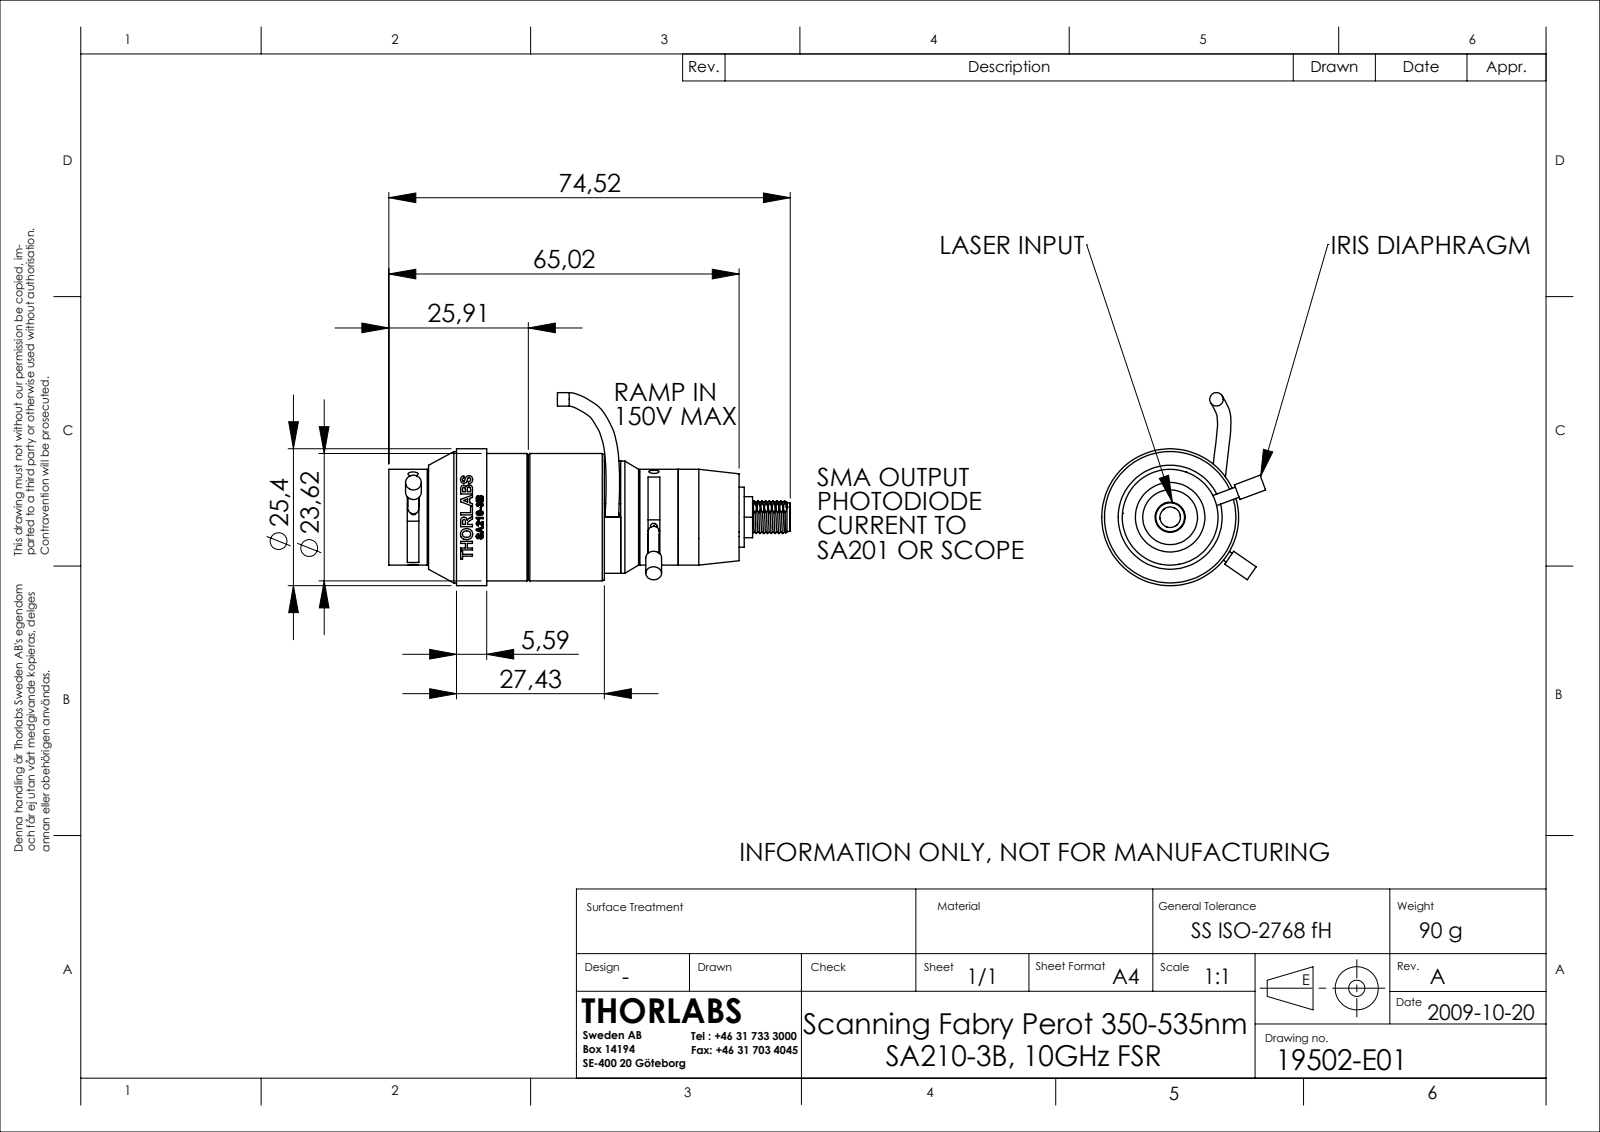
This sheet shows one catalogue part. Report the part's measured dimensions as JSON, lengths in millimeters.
{"part_name": "8655-013; 6902-E0W; kabel; SW3dPS-SMA Nut (+7 more)", "step_written_by": "SolidWorks 2009 (CONFIG_CONTROL_DESIGN)", "units": "millimeters", "bodies": {"solids": 9, "faces": 415, "planar": 160, "cylindrical": 180, "other": 75}, "overall_size": [74.52, 35.82, 30.41], "volume_mm3": 7613, "surface_area_mm2": 14572, "round_holes": [[1.48, 10], [1.91, 6], [1, 1], [2.7, 1], [3.81, 1], [4.6, 1], [5.59, 1], [6.1, 1], [6.35, 1], [8.26, 1], [9.78, 1], [10.03, 1]], "round_bosses_or_shafts": [[2.92, 2], [1.98, 2], [25.4, 1], [24.38, 1], [23.62, 1], [23.37, 1], [23, 1], [20.83, 1]], "partial_cylinders_radius": [[0.36, 1], [0.5, 1], [1.4, 1], [1.59, 1], [1.91, 1], [2.8, 1], [3.17, 1], [7.16, 1]], "face_to_face_distances": [7.37, 2.54, 43.82, 3.81, 46.36, 2.03, 3.3, 32.64, 40.01, 11.18], "hole_center_spacings": [3.77, 6.53, 7.54, 3.48, 6.69, 0.33, 4.06, 6.36]}
